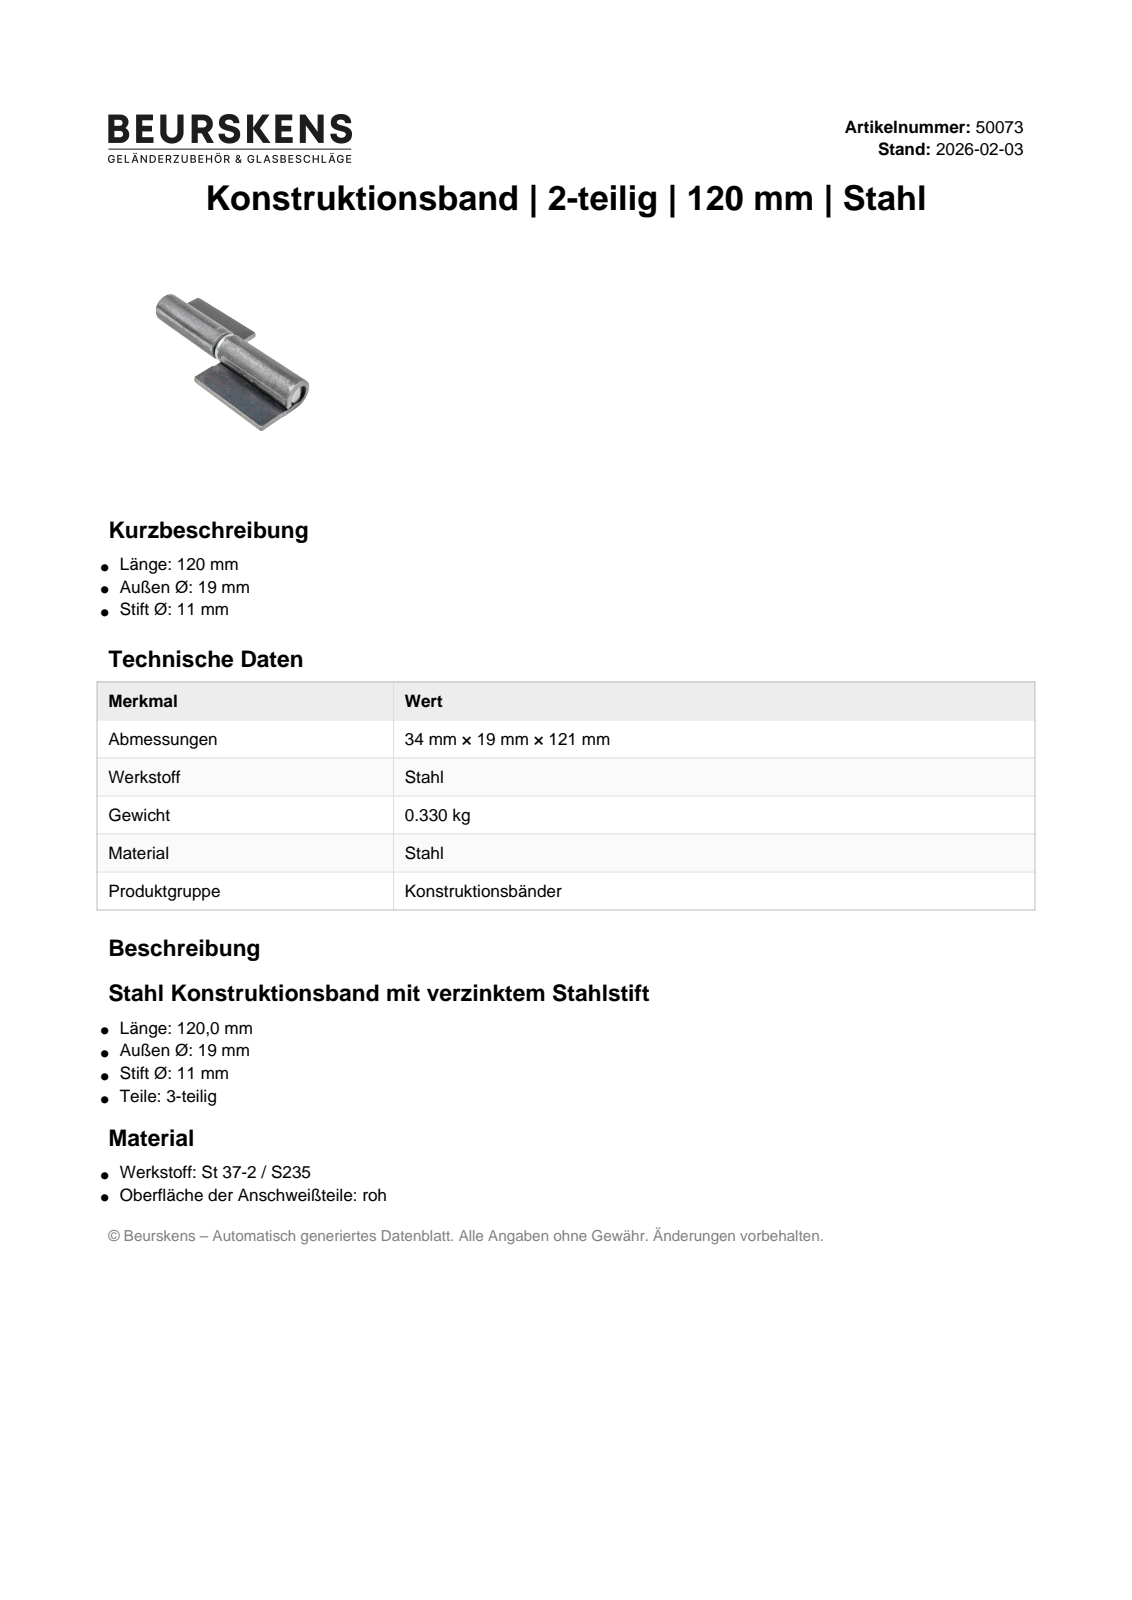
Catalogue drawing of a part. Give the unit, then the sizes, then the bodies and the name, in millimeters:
Units: millimetres
Overall size (bounding box): 120 × 45.3 × 30.23
Round holes (diameter × count): ⌀11 ×1
Round bosses / shafts (diameter × count): ⌀19 ×1
Main face-to-face distances: 4, 58.5, 61.5, 3, 120, 50
Volume: 41 960 mm³ · Surface area: 21 671 mm²
Bodies: 3 solids, 25 faces (16 planar, 6 cylindrical, 3 other)
Part name (STEP PRODUCT): 50073; 50073 Stift; 50073 Lasche
STEP written by: Autodesk Inventor 2023 (AUTOMOTIVE_DESIGN)
